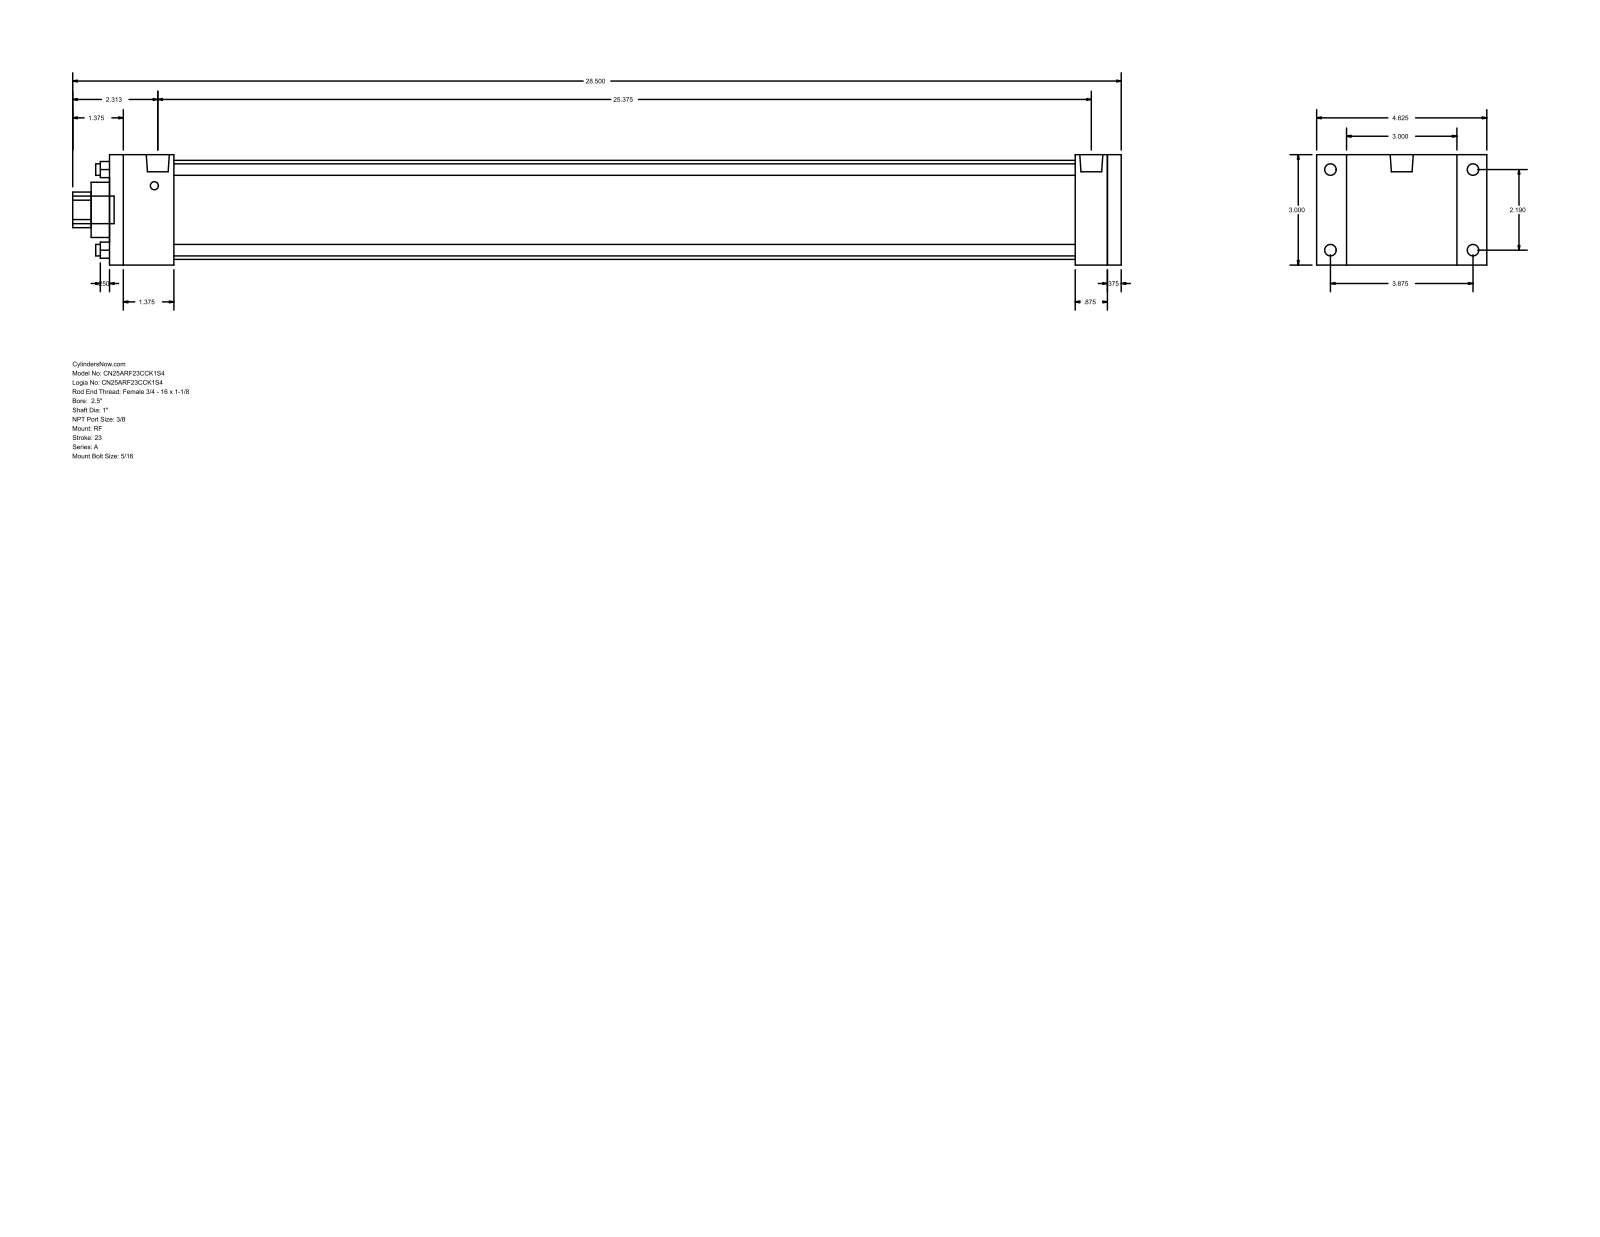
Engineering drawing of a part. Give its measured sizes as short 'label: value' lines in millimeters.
name: A_RF__0250_1
written by: GSSL Pune (CONFIG_CONTROL_DESIGN)
unit: mm
bodies: 0 solids, 92 faces (64 planar, 28 cylindrical, 0 other)
size: 723.9 × 117.47 × 76.2
holes: 4× ⌀7.94, 1× ⌀25.4, 1× ⌀38.1, 1× ⌀68.33
bosses: 4× ⌀7.94, 4× ⌀5.56, 2× ⌀15.93, 1× ⌀19.05
rounds: 1× R12.29
face distances: 76.2, 698.5, 9.52, 688.98, 44.45, 666.75, 622.3, 644.53, 654.05, 22.23
hole spacings: 39.33, 55.62, 78.66
